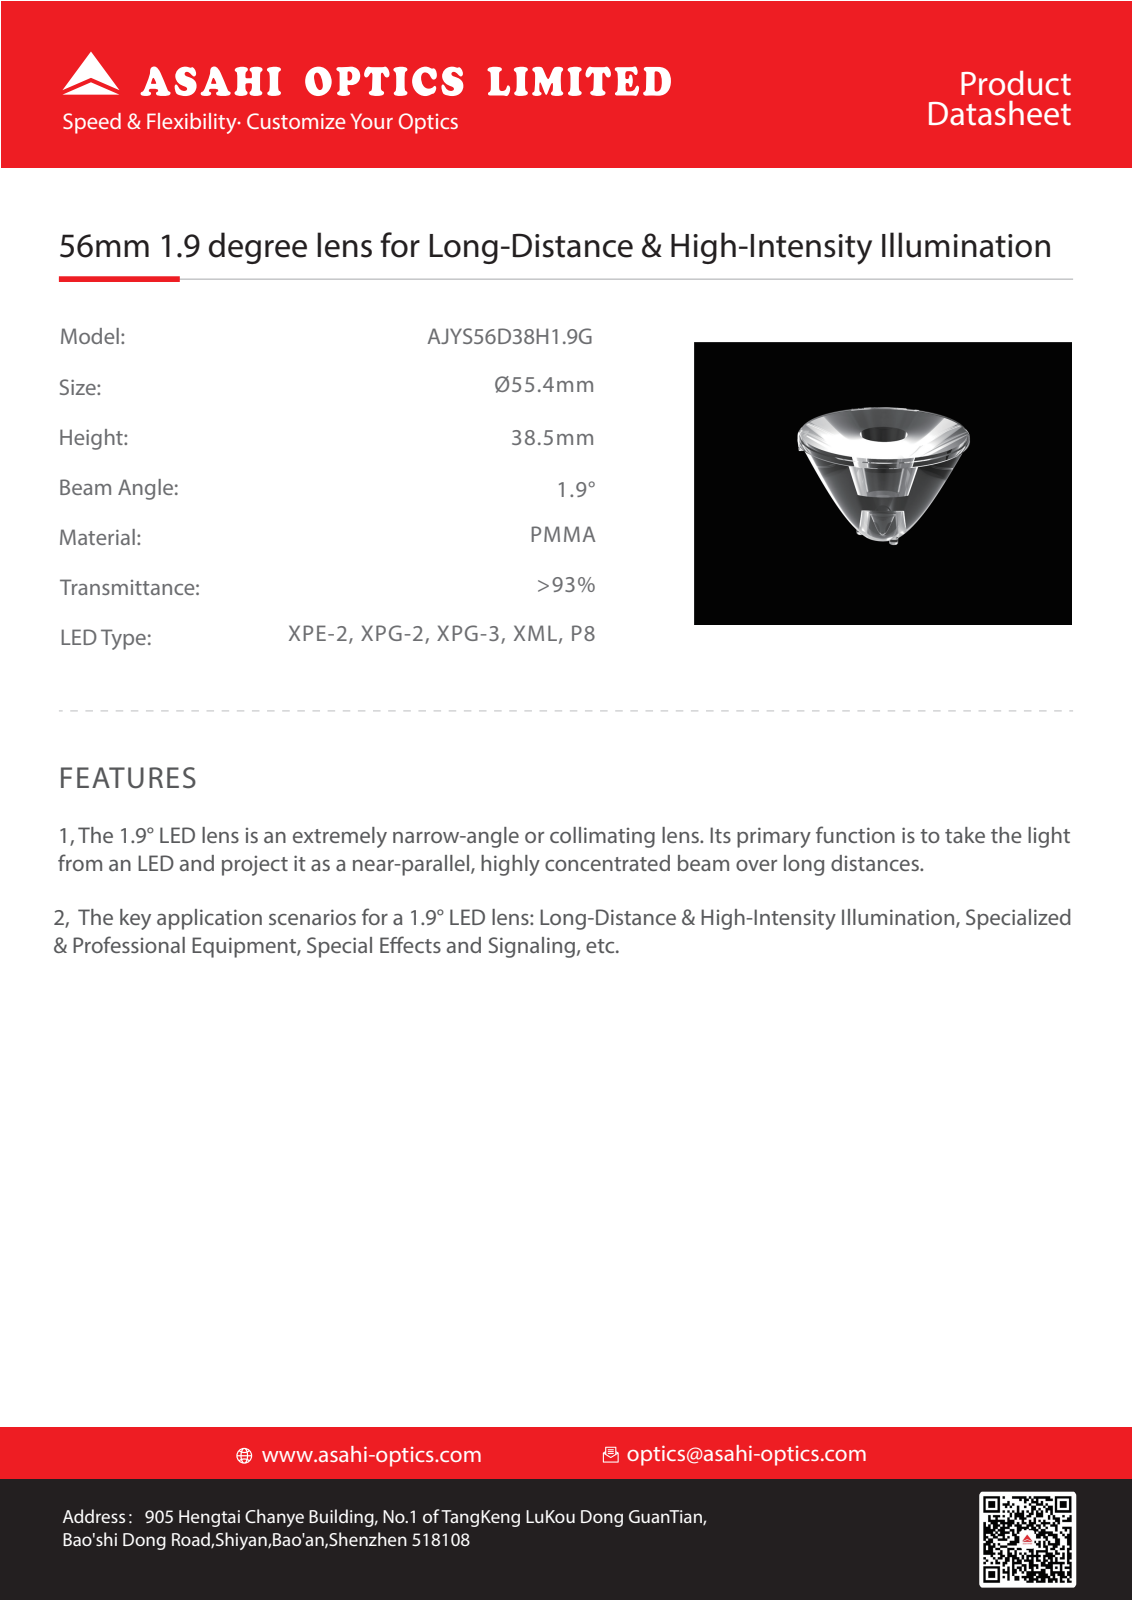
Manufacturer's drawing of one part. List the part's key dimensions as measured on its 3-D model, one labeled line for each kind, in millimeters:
Part name (STEP PRODUCT): Admi21A8E13196te
STEP written by: SIEMENS PLM Software NX 10.0 (AP203_CONFIGURATION_CONTROLLED_3D_DESIGN_OF_MECHANICAL_PARTS_AND_ASSEMBLIES_MIM_LF)
Units: millimetres
Bodies: 1 solid, 29 faces (10 planar, 2 cylindrical, 17 other)
Overall size (bounding box): 55.4 × 55.4 × 38.49
Volume: 42 899 mm³ · Surface area: 8 389 mm²
Partial cylindrical surfaces — rounded edges, fillets, slot ends (radius × count): R0.5 ×2
Main face-to-face distances: 1.5, 32, 35, 36.5, 4.5, 30.5, 5.5, 1, 36, 37.5
